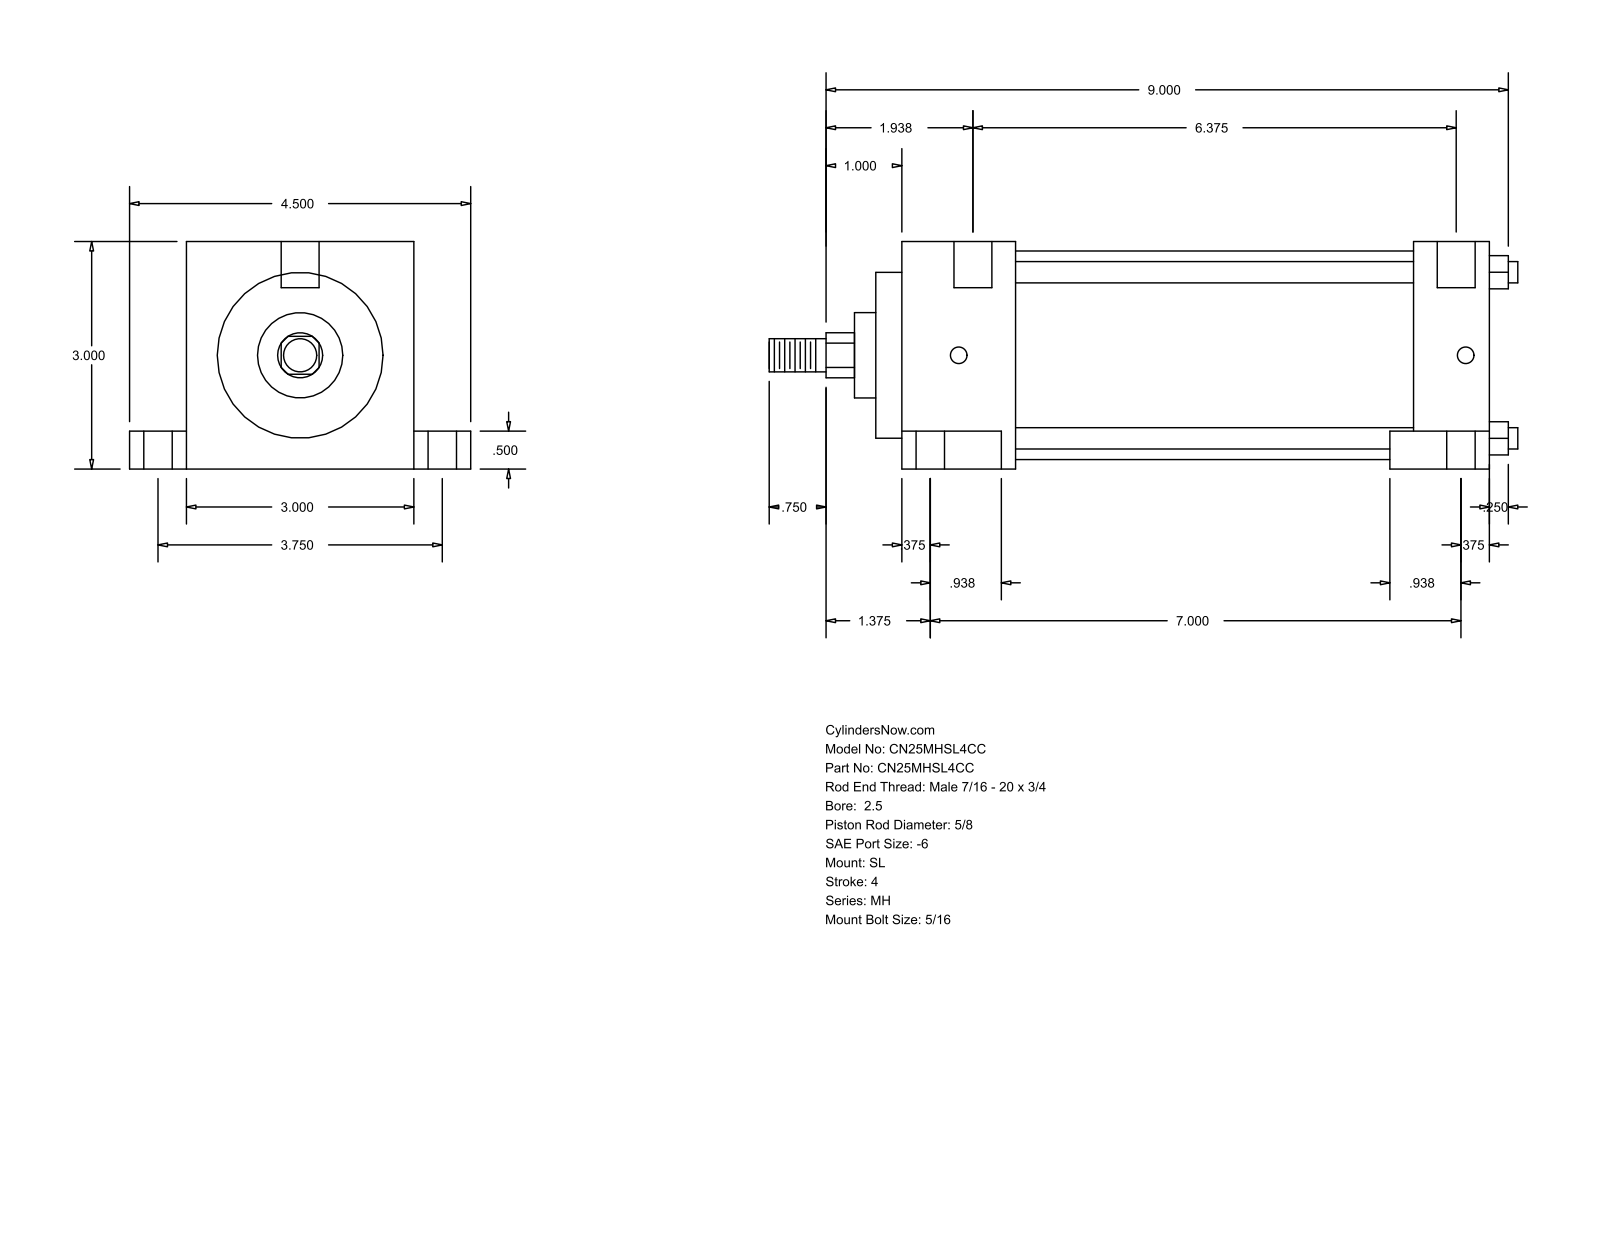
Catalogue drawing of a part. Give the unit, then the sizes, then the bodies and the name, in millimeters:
Units: millimetres
Overall size (bounding box): 250.82 × 114.3 × 76.2
Round holes (diameter × count): ⌀5.56 ×2, ⌀9.53 ×2, ⌀15.88 ×2, ⌀12.7 ×1
Round bosses / shafts (diameter × count): ⌀7.14 ×4, ⌀69.85 ×1, ⌀55.55 ×1, ⌀28.57 ×1, ⌀15.88 ×1, ⌀11.11 ×1
Partial cylindrical surfaces — rounded edges, fillets, slot ends (radius × count): R7.54 ×1
Main face-to-face distances: 76.2, 25.4, 180.18, 205.58, 63.5, 12.7, 19.05, 95.25, 31.75, 172.24
Hole centre spacings: 47.65, 3.17, 95.24
Bodies: 0 solids, 86 faces (61 planar, 25 cylindrical, 0 other)
Part name (STEP PRODUCT): MH_SL__0250_0.625
STEP written by: GSSL Pune (CONFIG_CONTROL_DESIGN)
